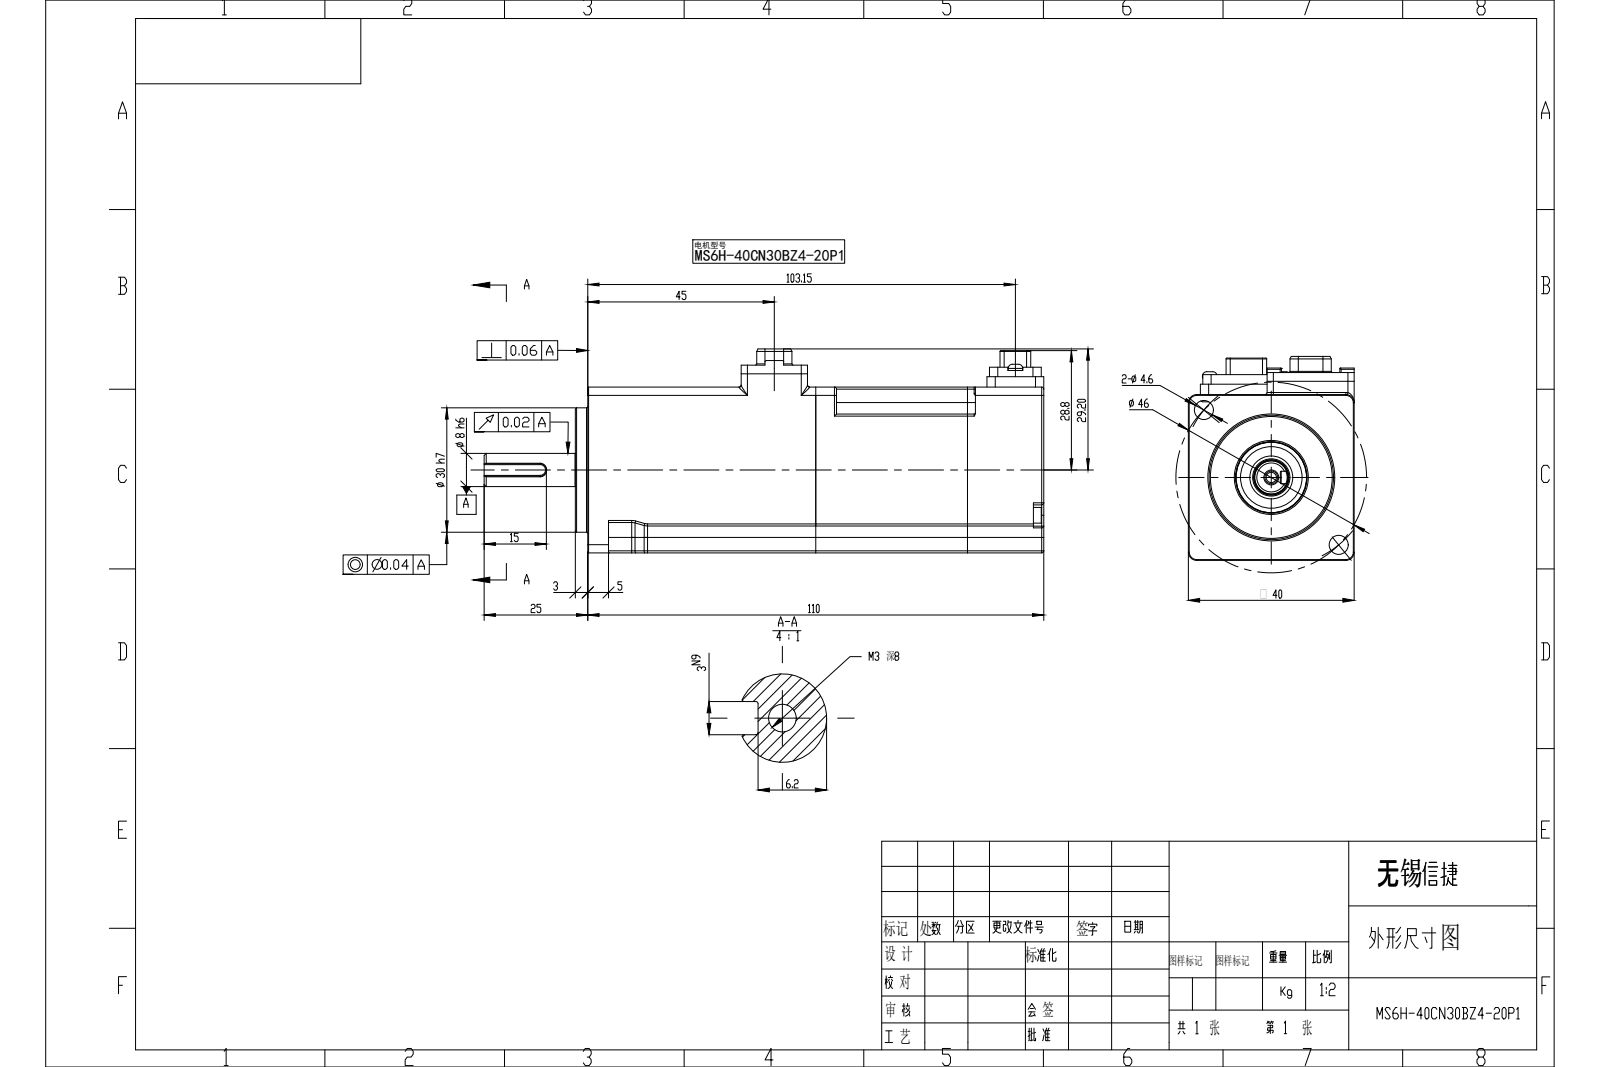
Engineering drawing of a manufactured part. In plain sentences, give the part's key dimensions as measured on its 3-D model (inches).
The part is named "MS6H-40CN30BZ3-20P1-S". Its 3-D file was written by "SolidWorks 2022 (AUTOMOTIVE_DESIGN)". It is 0 solids with 646 faces: 314 planar, 220 cylindrical and 112 other. Overall it measures 5.315 by 1.937 by 1.575 inches. Round holes: 8 of diameter 0.083, 2 of diameter 0.063, 2 of diameter 0.106, 2 of diameter 0.181, 1 of diameter 0.098, 1 of diameter 0.354, 1 of diameter 0.585. Round bosses or shafts: 4 of diameter 0.15, 2 of diameter 0.138, 1 of diameter 1.181, 1 of diameter 0.669, 1 of diameter 0.407, 1 of diameter 0.335, 1 of diameter 0.315. Partial cylindrical surfaces (rounded edges, fillets, slot ends): 56 of radius 0.02, 18 of radius 0.012, 16 of radius 0.079, 13 of radius 0.008, 8 of radius 0.118, 5 of radius 0.059, 4 of radius 0.039, 4 of radius 0.098. The main face-to-face distances are 1.575, 1.319, 0.256, 1.063, 4.331, 2.165, 0.118, 4.449, 2.283, 0.11. The hole center spacings are 0.23, 0.708, 0.906, 1.28, 0.669, 0.315, 0.461, 0.654.
